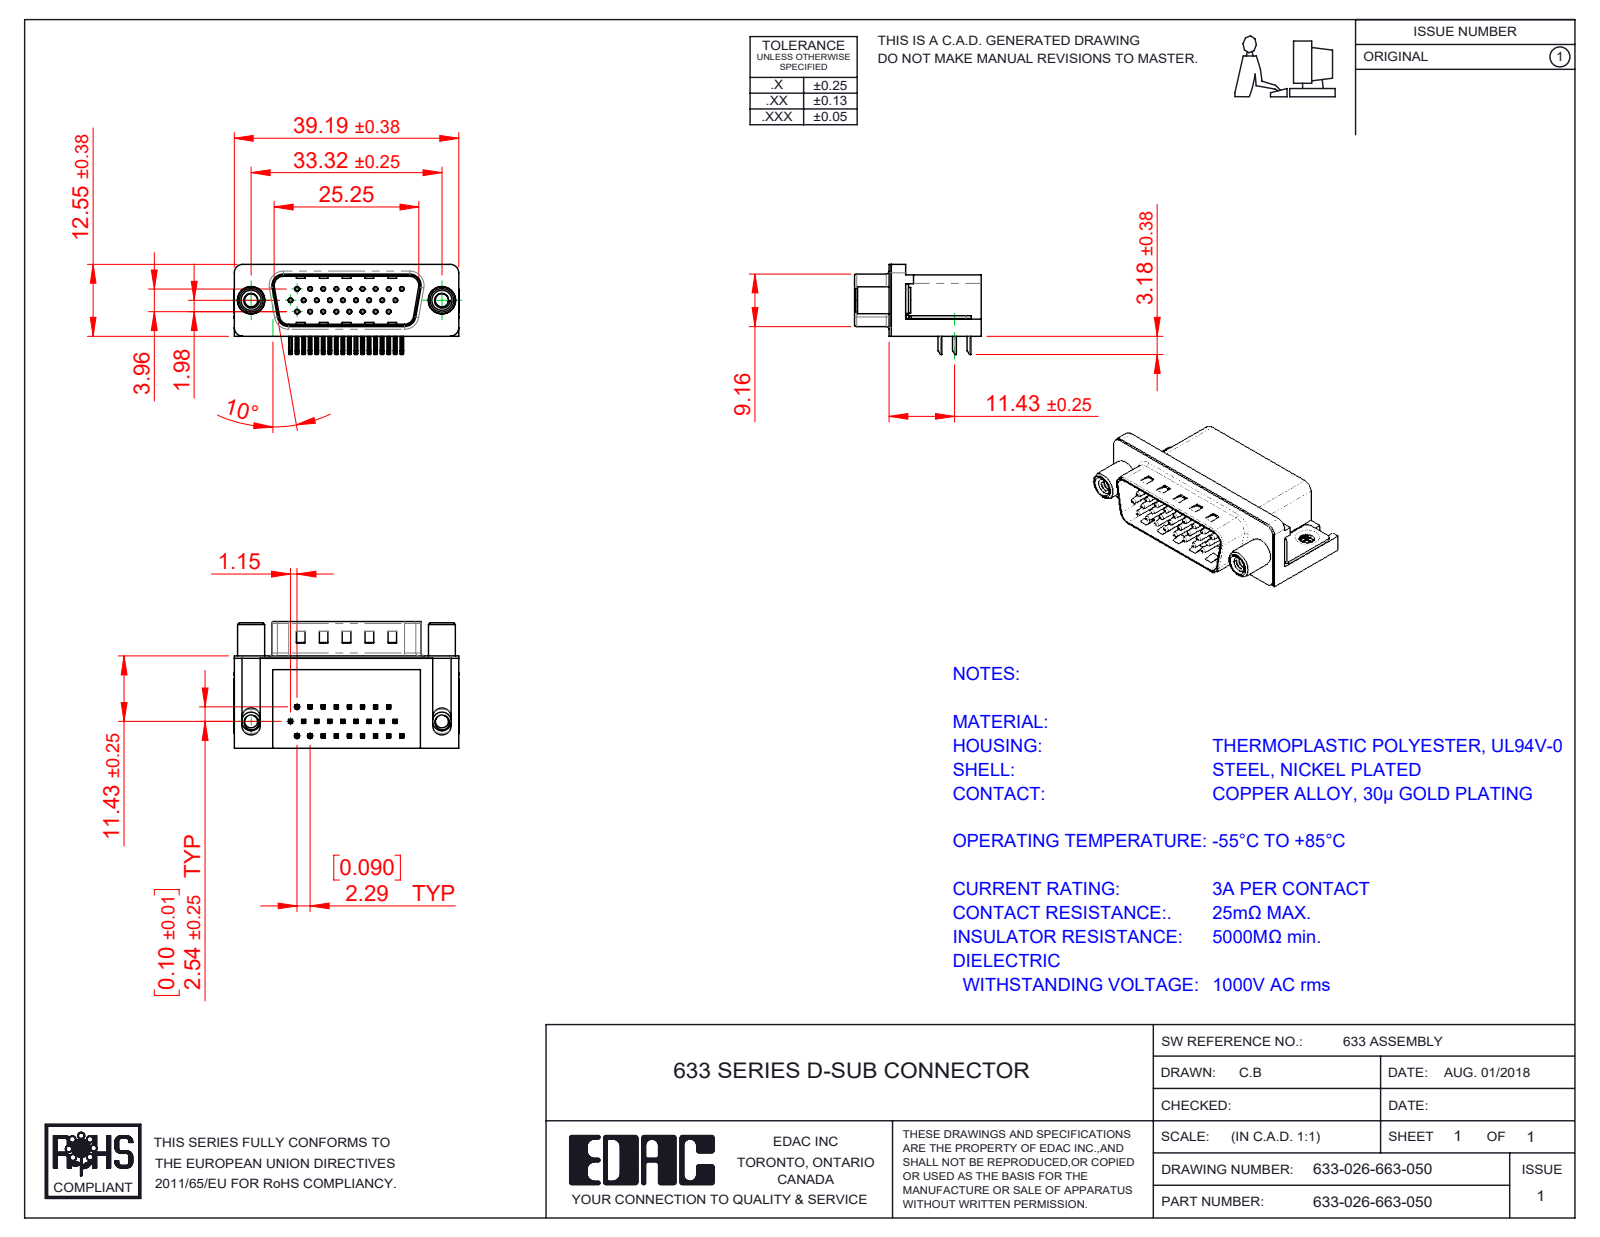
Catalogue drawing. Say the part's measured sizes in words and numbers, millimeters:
The part is named "633 Contact Top; 633 Housing_26 Contact; 633 Contact Bottom; 633-026-663-050 (+4 more)". Its 3-D file was written by "SolidWorks 2016 (CONFIG_CONTROL_DESIGN)". It is 32 solids with 2328 faces: 1413 planar, 698 cylindrical and 217 other. Overall it measures 39.22 by 22.1 by 15.73 millimeters. Its volume is 5 700 cubic millimeters and its surface area 7 529 square millimeters. Round holes: 26 of diameter 0.35, 26 of diameter 0.8, 2 of diameter 2.26, 2 of diameter 2.3, 2 of diameter 3.1, 2 of diameter 4, 2 of diameter 4.8, 2 of diameter 5. Round bosses or shafts: 26 of diameter 0.75, 2 of diameter 4.9, 2 of diameter 4.7, 2 of diameter 4.5, 2 of diameter 3.85, 2 of diameter 3.26. Partial cylindrical surfaces (rounded edges, fillets, slot ends): 104 of radius 0.25, 52 of radius 0.12, 16 of radius 1, 9 of radius 0.5, 8 of radius 1.5, 8 of radius 1.6, 4 of radius 0.9, 4 of radius 2. The main face-to-face distances are 0.4, 10.35, 15.7, 2.9, 2.5, 16.1, 8.76, 0.35, 10.7, 13.2. The hole center spacings are 2.29, 4.57, 2.28, 3.96, 6.05, 4.58, 6.86, 7.92.
